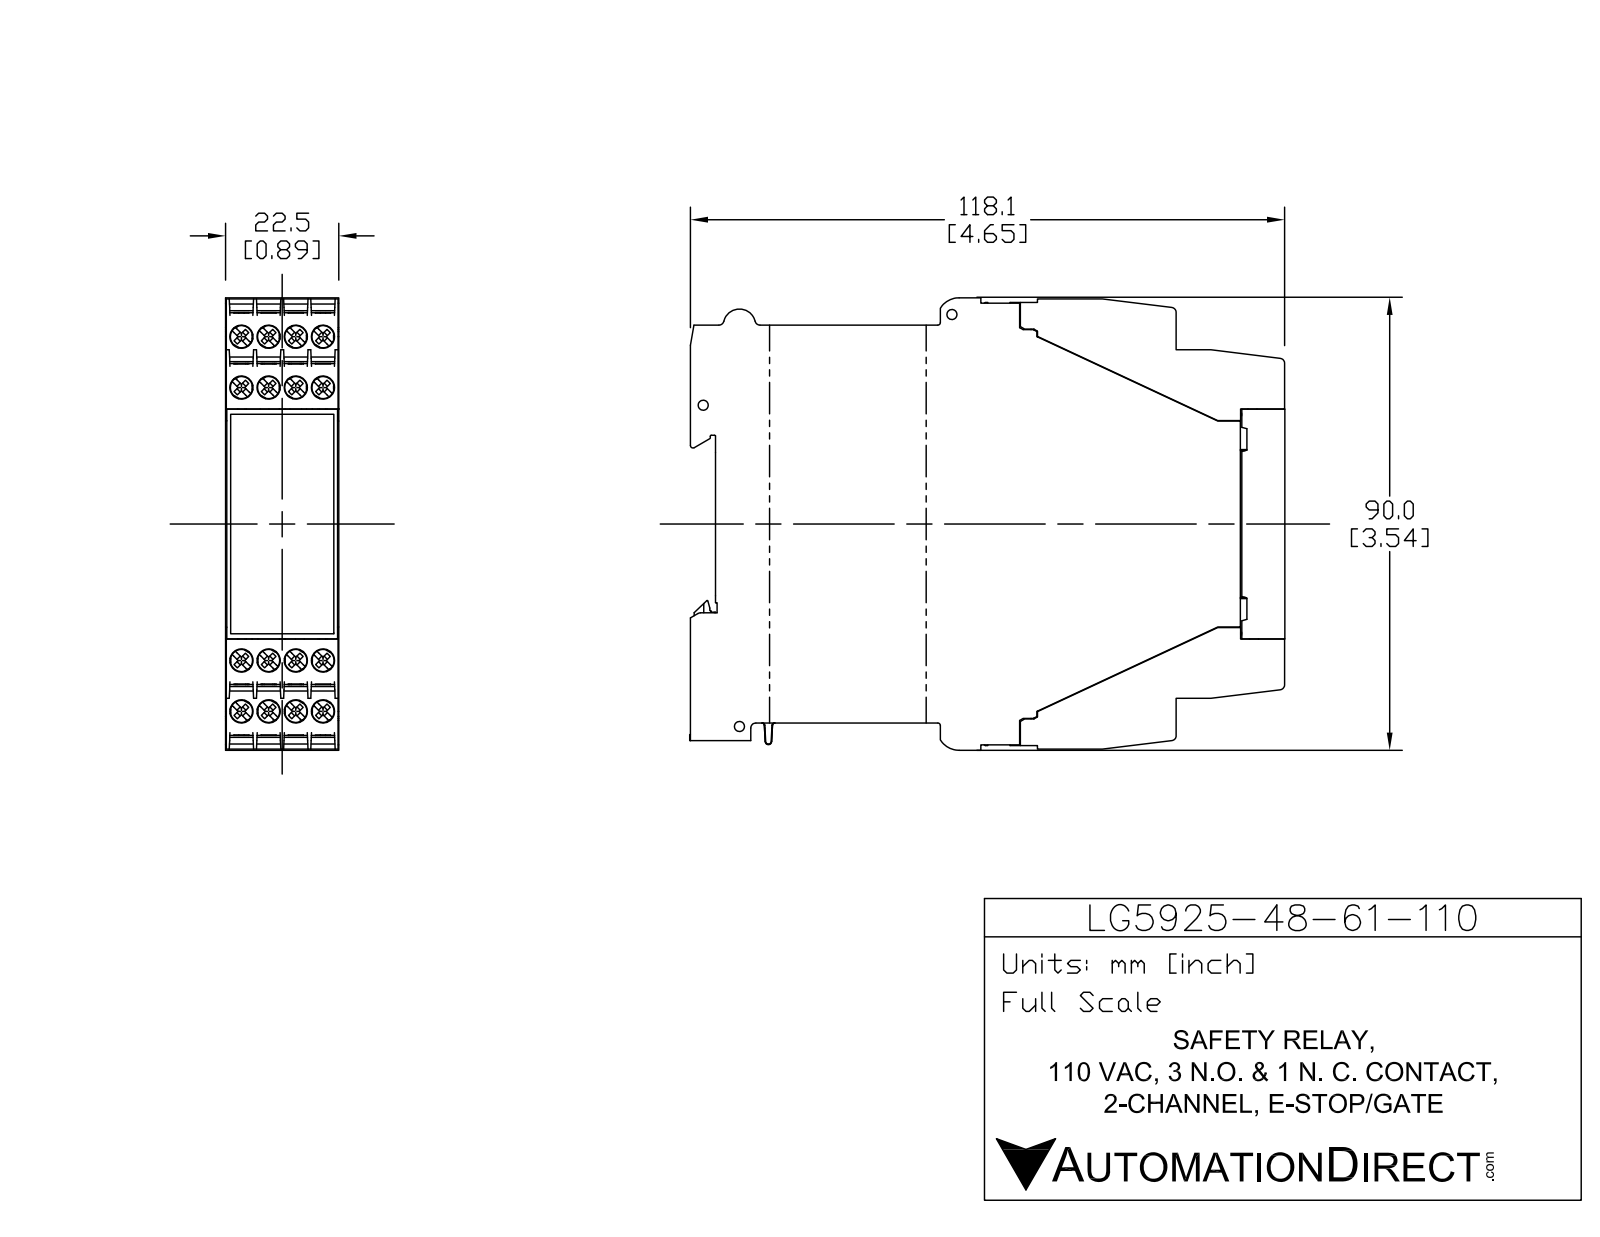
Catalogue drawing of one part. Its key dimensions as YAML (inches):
part_name: "LG5925-48-61-110"
step_written_by: "SolidWorks 2017 (AUTOMOTIVE_DESIGN)"
units: inches
bodies: {solids: 18, faces: 940, planar: 815, cylindrical: 83, other: 42}
overall_size: [4.646, 4.01, 0.906]
volume: 14.56
surface_area: 73.74
round_holes:
  - {diameter: 0.039, count: 4}
  - {diameter: 0.067, count: 4}
  - {diameter: 0.049, count: 1}
round_bosses_or_shafts:
  - {diameter: 0.053, count: 1}
partial_cylinders:
  - {radius: 0.004, count: 10}
  - {radius: 0.039, count: 8}
  - {radius: 0.02, count: 7}
  - {radius: 0.005, count: 6}
  - {radius: 0.004, count: 4}
  - {radius: 0.008, count: 3}
  - {radius: 0.021, count: 3}
  - {radius: 0.012, count: 2}
face_to_face_distances: [0.906, 0.896, 0.398, 0.9, 0.89, 2.346, 0.183, 2.927, 0.848, 0.581]
hole_center_spacings: [0.638, 0.848, 1.061]
